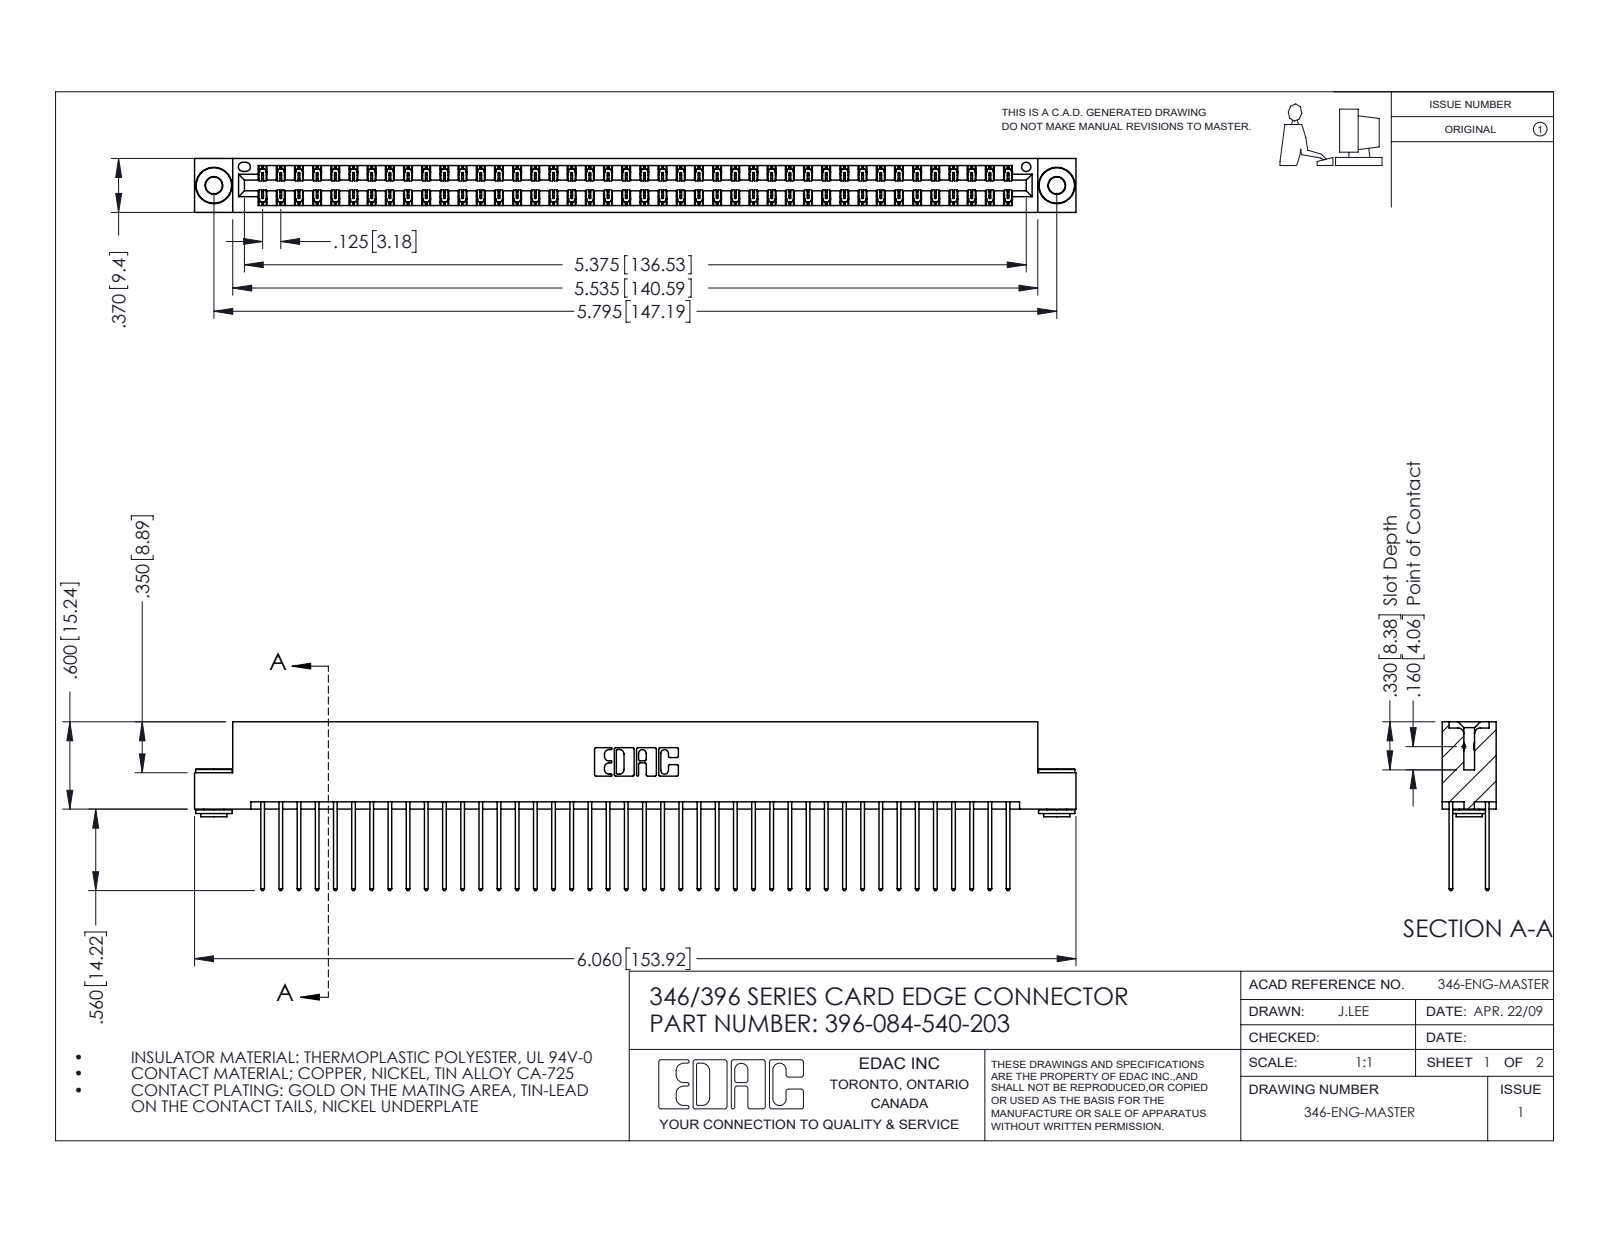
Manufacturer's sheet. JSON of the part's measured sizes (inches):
{"part_name": "345-250-002_345-250-002-102; 345-292-001_345-293-140; 396-084-540-203; 346 Part_Flush Mounting Lugs - 0.156 Dia-TH", "step_written_by": "SolidWorks 2016 (CONFIG_CONTROL_DESIGN)", "units": "inches", "bodies": {"solids": 87, "faces": 4528, "planar": 3026, "cylindrical": 1494, "other": 8}, "overall_size": [6.06, 1.16, 0.37], "volume_in3": 0.937, "surface_area_in2": 35.37, "round_holes": [[0.116, 2], [0.156, 2], [0.064, 1]], "round_bosses_or_shafts": [[0.25, 2], [0.18, 2], [0.136, 2]], "partial_cylinders_radius": [[0.006, 126], [0.01, 84], [0.01, 22], [0.007, 6], [0.031, 6], [0.026, 3], [0.014, 2], [0.022, 2]], "face_to_face_distances": [0.048, 0.322, 0.25, 0.025, 0.072, 0.298, 0.37, 0.275, 0.148, 0.222], "hole_center_spacings": [0.246, 5.586, 5.795]}
